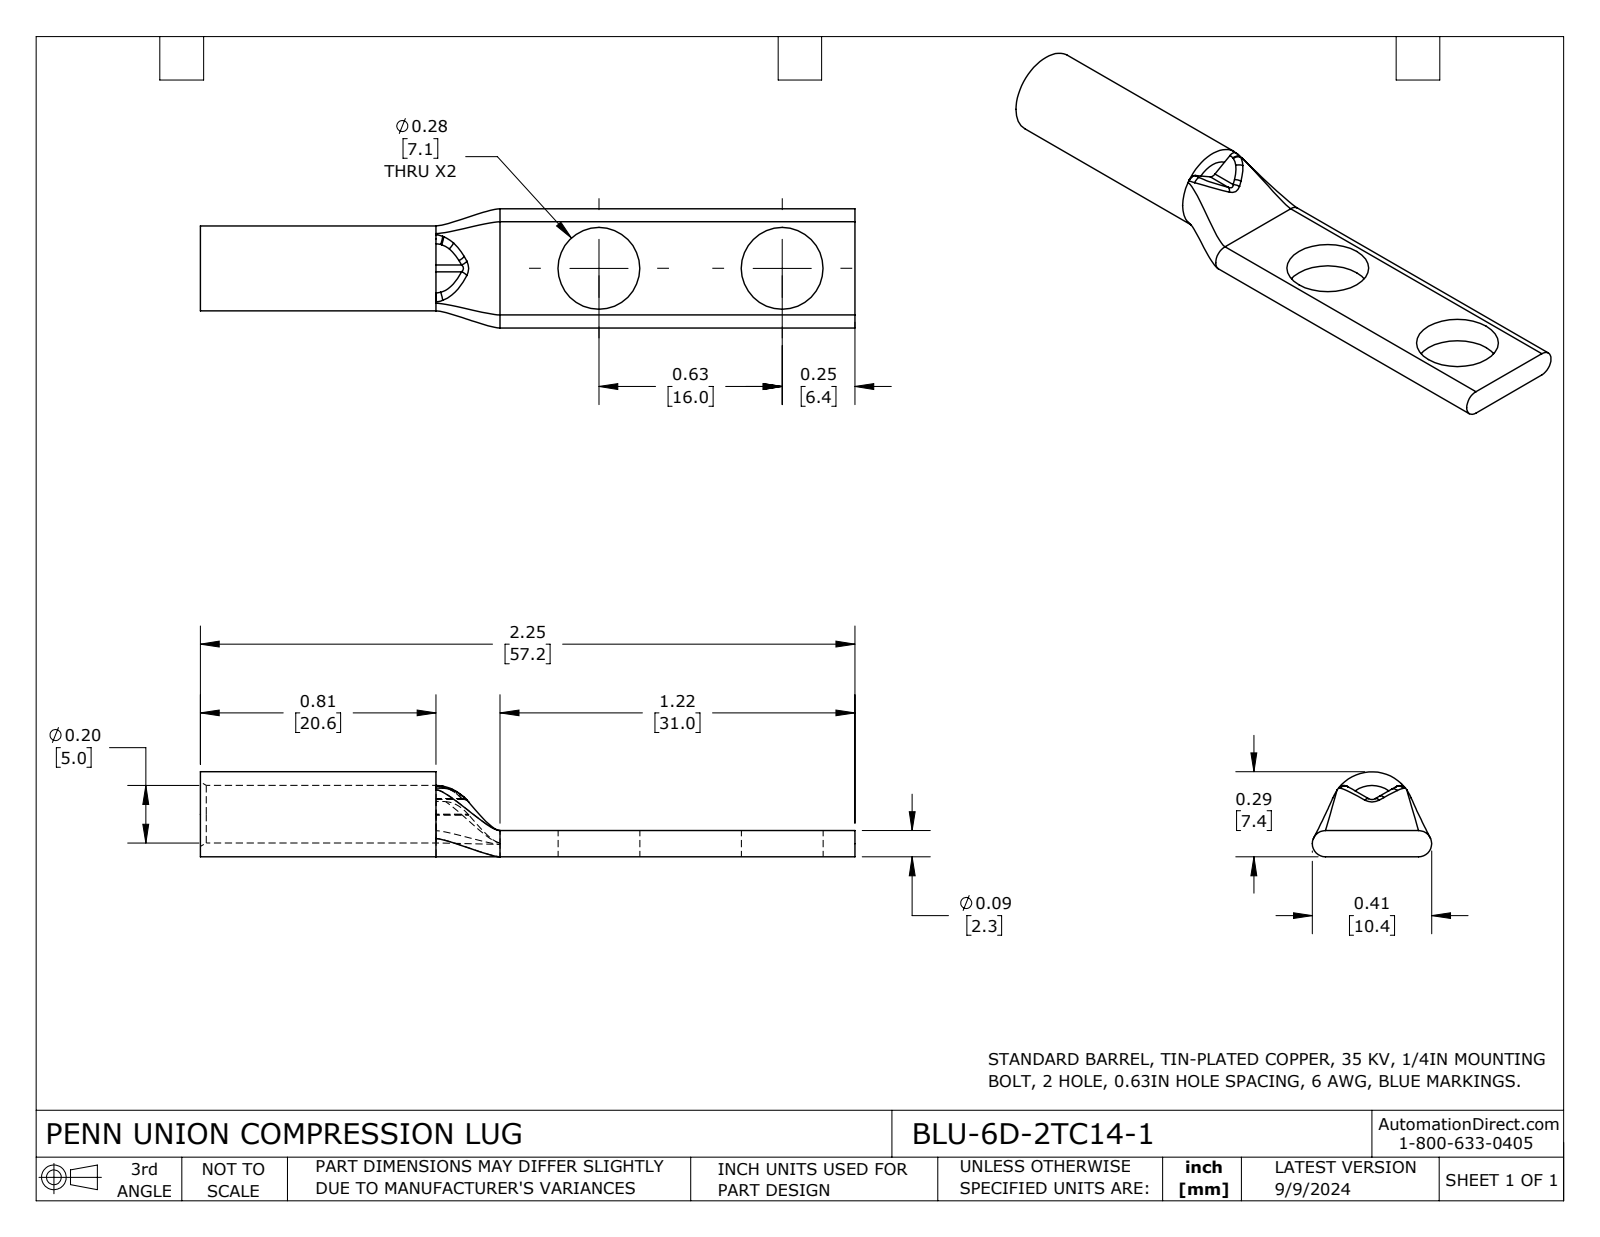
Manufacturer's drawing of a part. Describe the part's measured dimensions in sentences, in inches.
The part is named "BLU-6D-2TC14-1". Its 3-D file was written by "SolidWorks 2023 (CONFIG_CONTROL_DESIGN)". It is 1 solid with 43 faces: 11 planar, 13 cylindrical and 19 other. Overall it measures 2.25 by 0.41 by 0.292 inches. Its volume is 0.068 cubic inches and its surface area 2.736 square inches. Round holes: 2 of diameter 0.281, 1 of diameter 0.198. Round bosses or shafts: 1 of diameter 0.292. Partial cylindrical surfaces (rounded edges, fillets, slot ends): 2 of radius 0.024, 2 of radius 0.045. The main face-to-face distances are 0.09, 2.25, 0.81, 1.44, 0.047, 1.03, 0.22, 1.22. The hole center spacings are 0.63.
